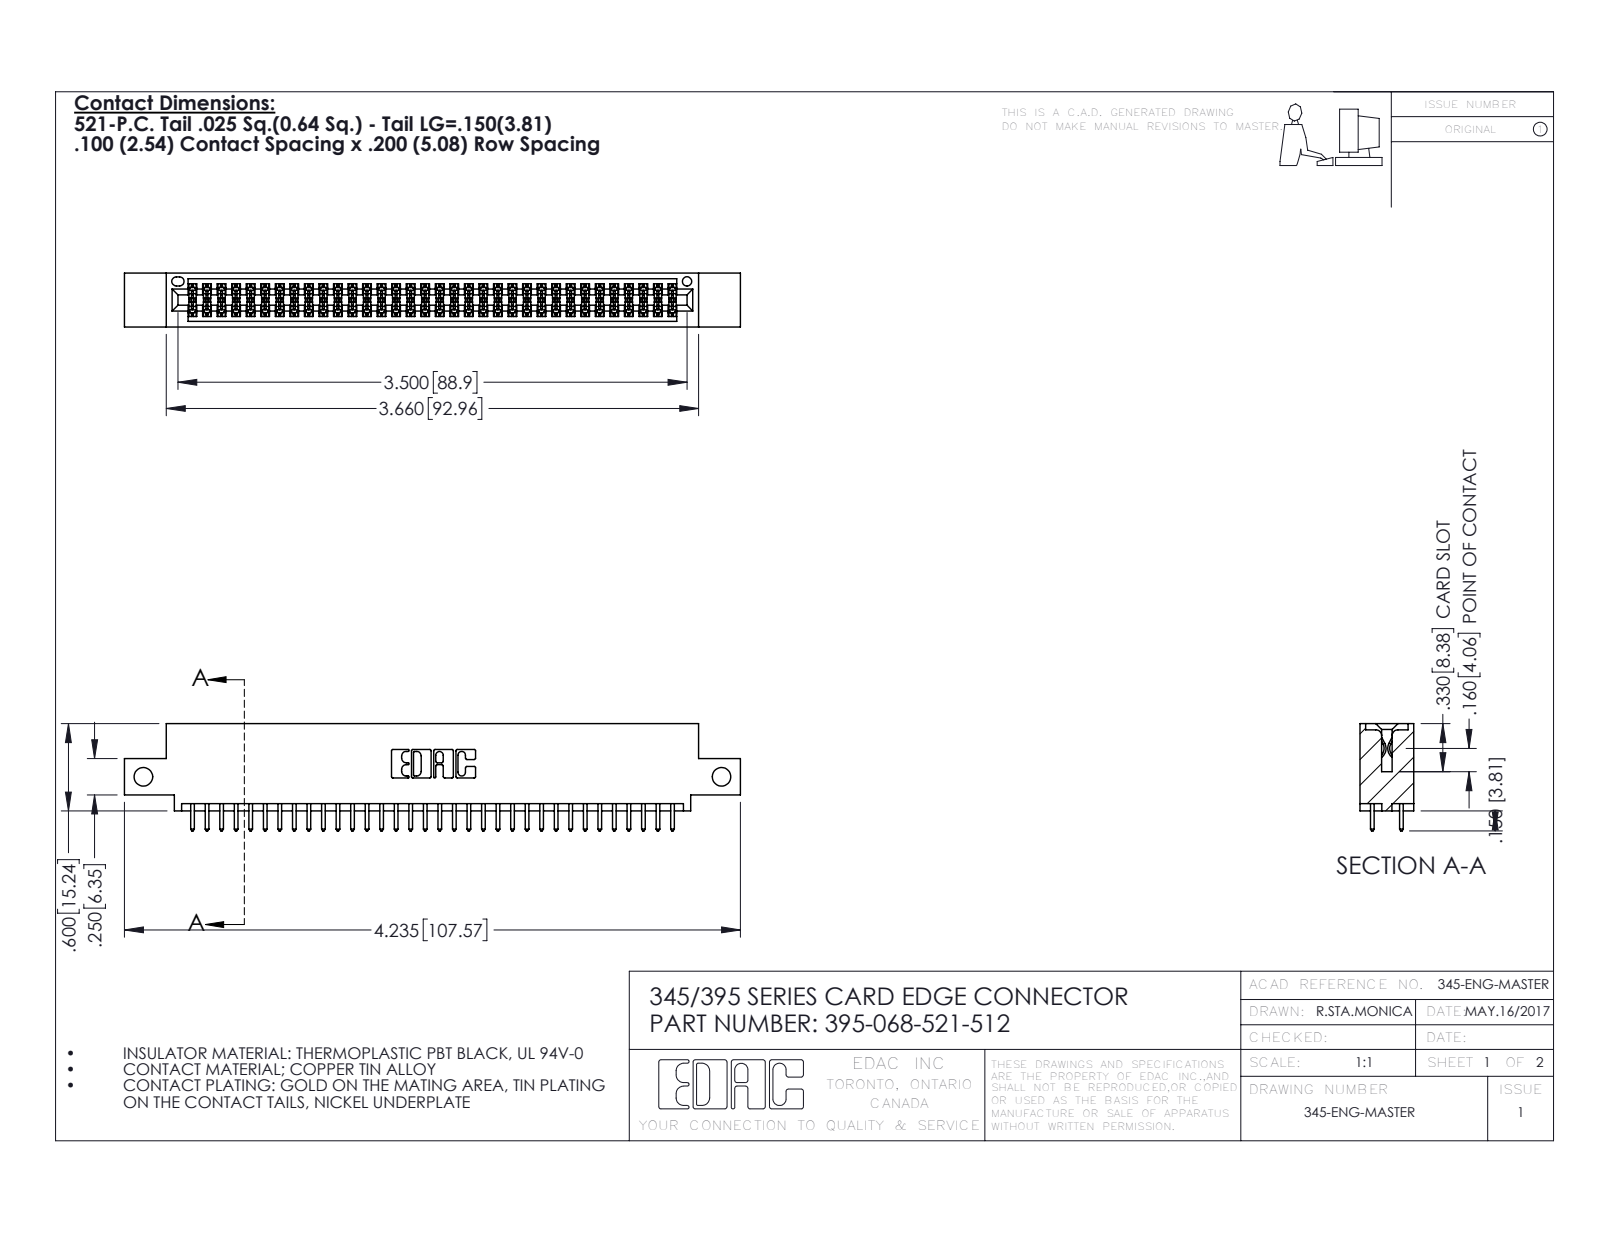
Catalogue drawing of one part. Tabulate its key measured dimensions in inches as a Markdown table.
| quantity | value |
| --- | --- |
| part name | 345 Part_0.110 Offset - Side Mount; 395-068-521-512; 345-292-001_345-293-121 |
| STEP written by | SolidWorks 2016 (CONFIG_CONTROL_DESIGN) |
| units | inches |
| bodies | 69 solids, 3530 faces (2328 planar, 1202 cylindrical, 0 other) |
| overall size | 4.235 × 0.737 × 0.37 |
| volume | 0.622 in³ |
| surface area | 22.75 in² |
| round holes (diameter × count) | 0.128 × 2, 0.064 × 1 |
| partial cylindrical surfaces (radius × count) | 0.006 × 102, 0.01 × 68, 0.01 × 22, 0.007 × 6, 0.031 × 6, 0.026 × 3, 0.014 × 2, 0.019 × 2 |
| main face-to-face distances | 0.298, 0.072, 0.2, 0.37, 0.098, 0.272, 0.025, 0.225, 0.175, 0.149 |
| hole center spacings | 3.975 |
